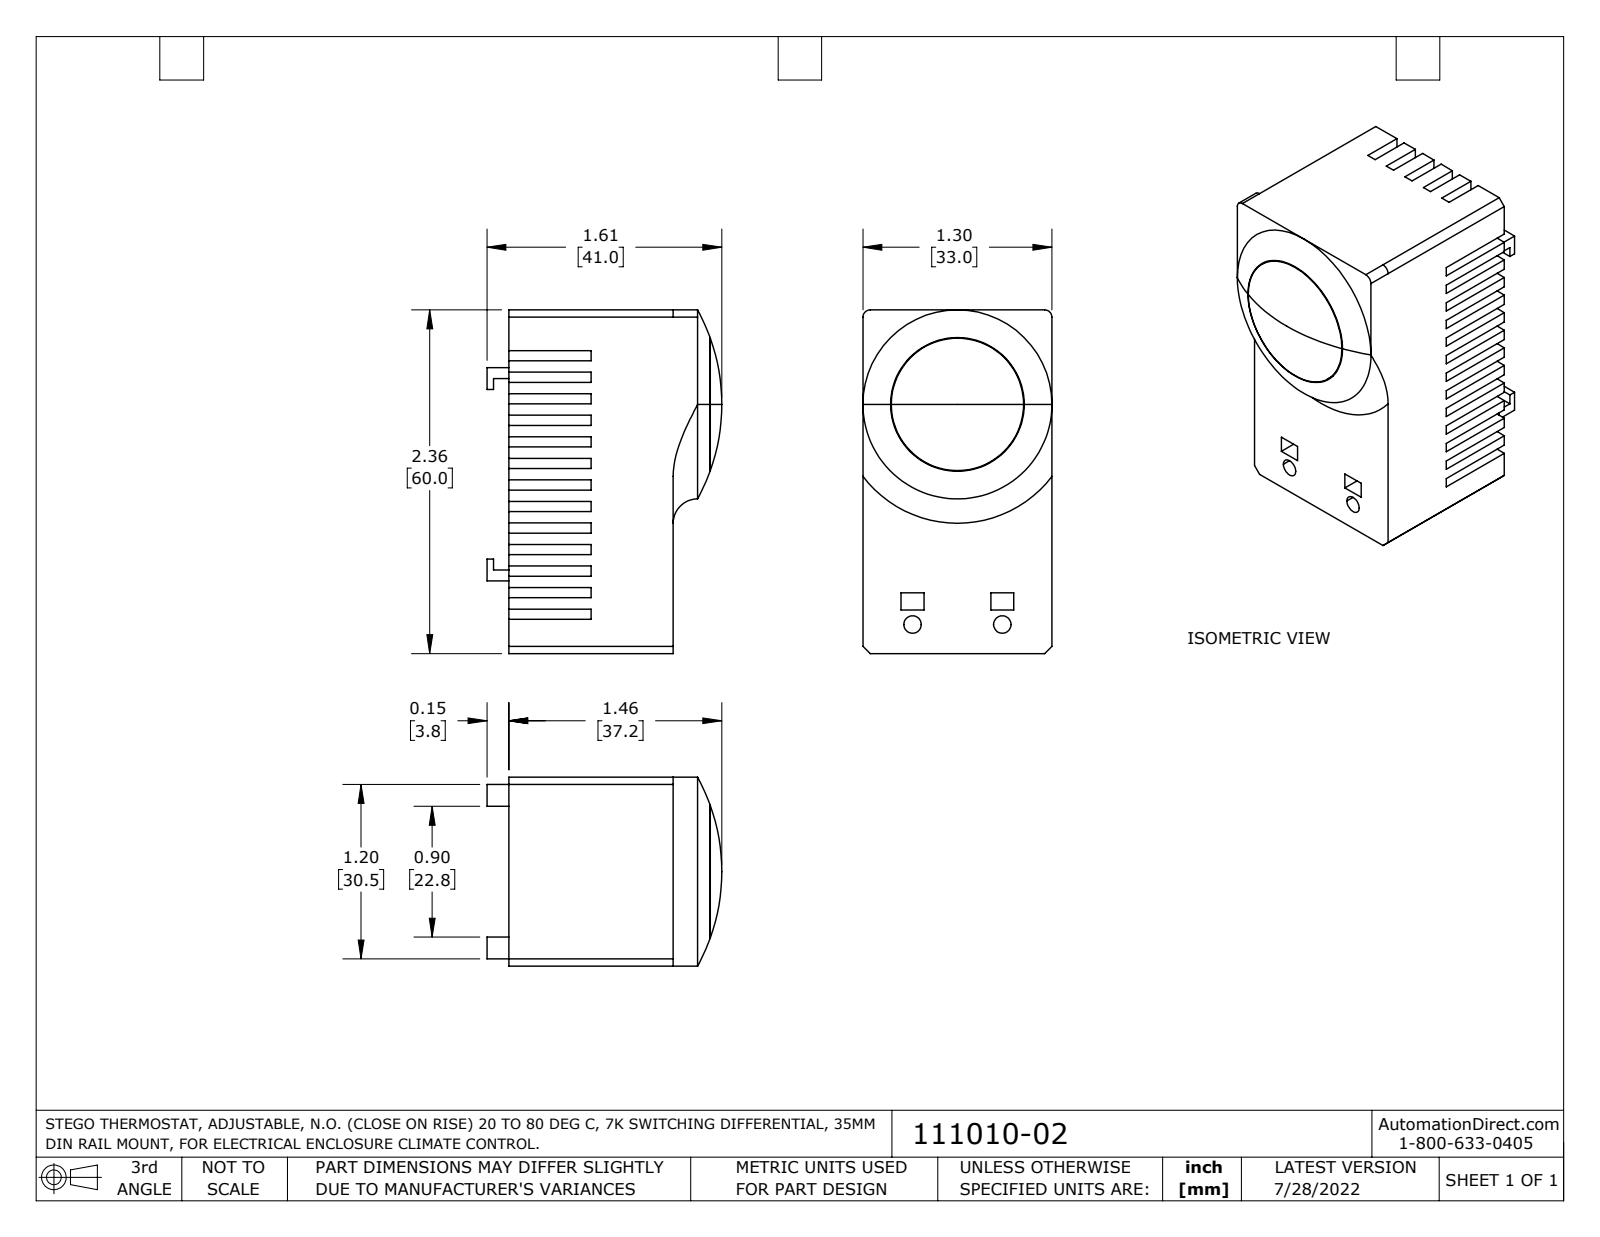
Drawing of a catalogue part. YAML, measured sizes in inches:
part_name: "111010-02_Default"
step_written_by: "SolidWorks 2021 (CONFIG_CONTROL_DESIGN)"
units: inches
bodies: {solids: 1, faces: 198, planar: 183, cylindrical: 10, other: 5}
overall_size: [2.362, 1.614, 1.299]
volume: 3.737
surface_area: 19.92
round_holes:
  - {diameter: 0.12, count: 2}
  - {diameter: 0.919, count: 1}
round_bosses_or_shafts:
  - {diameter: 0.909, count: 1}
partial_cylinders:
  - {radius: 0.05, count: 2}
face_to_face_distances: [1.299, 0.148, 0.07, 2.362, 0.296, 1.13, 0.444, 0.592, 0.078, 0.218]
hole_center_spacings: [1.544, 0.617]
